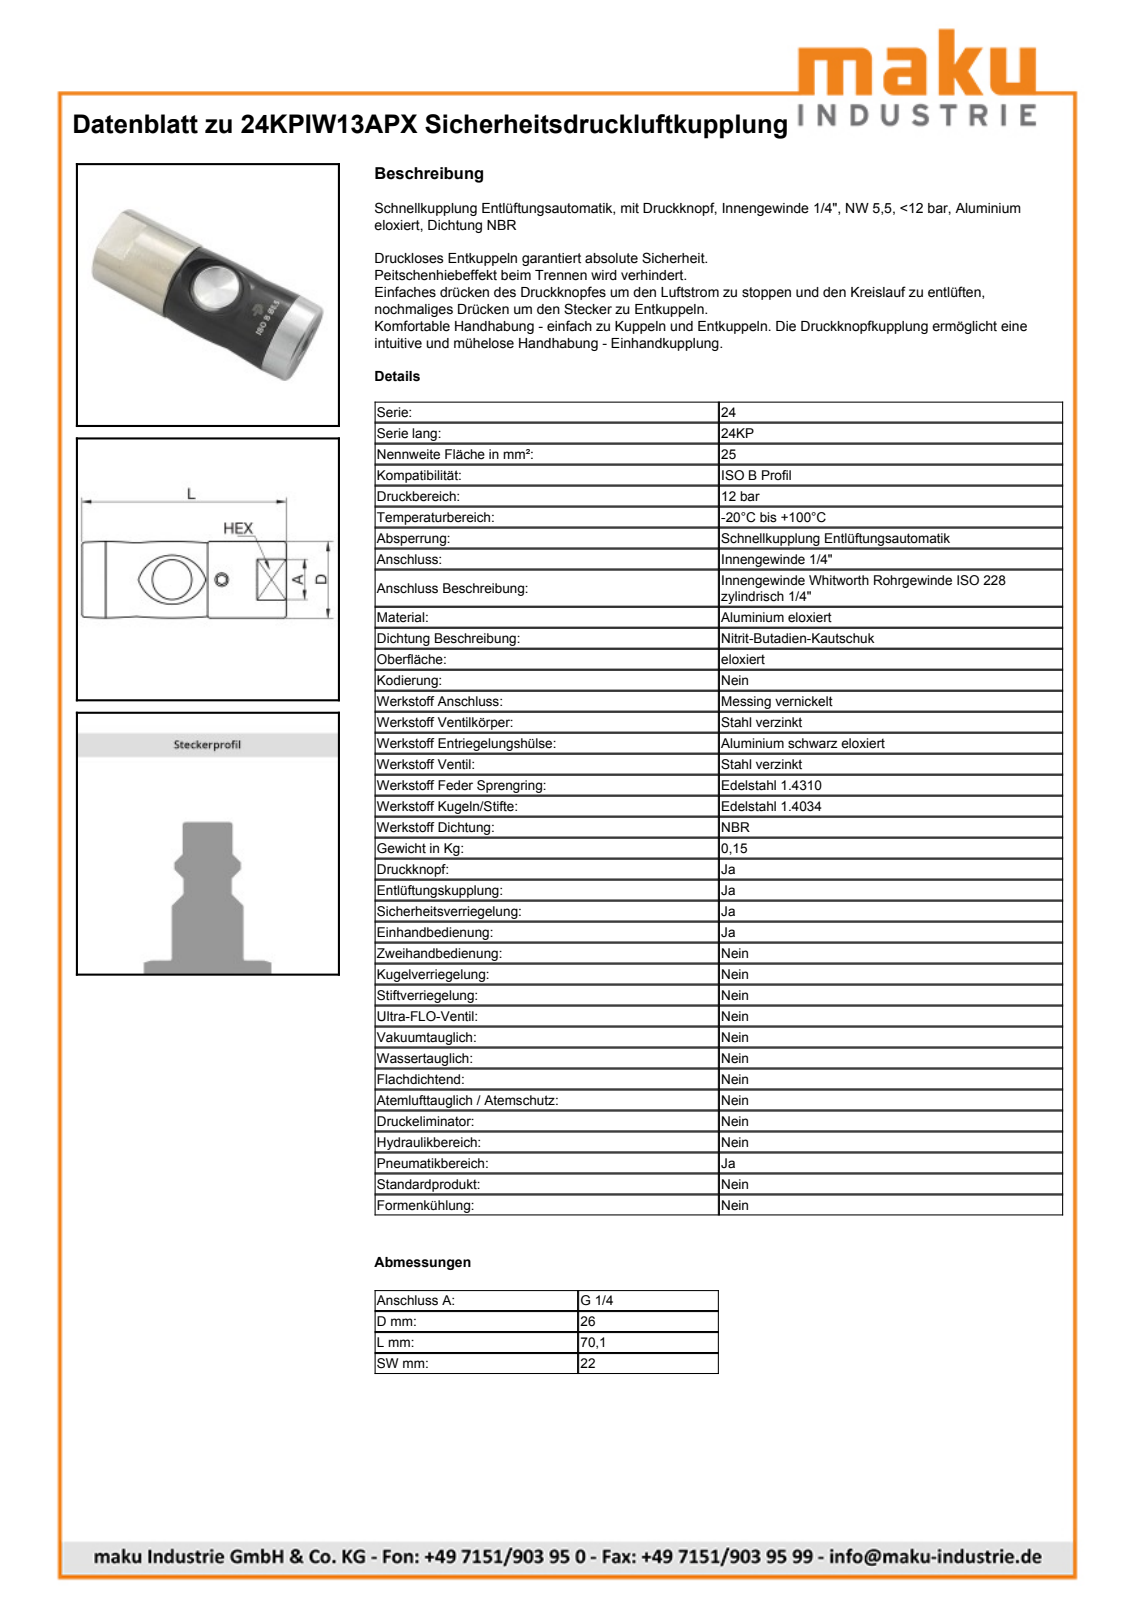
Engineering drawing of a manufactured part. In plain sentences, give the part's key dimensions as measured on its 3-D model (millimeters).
The part is named "24KPIW13APX". Its 3-D file was written by "Autodesk Inventor 2019 (CONFIG_CONTROL_DESIGN)". It is 41 solids with 266 faces: 74 planar, 88 cylindrical and 104 other. Overall it measures 70.1 by 26 by 26 millimeters. Its volume is 39 480 cubic millimeters and its surface area 24 201 square millimeters. Round holes: 2 of diameter 12.4, 1 of diameter 3.5, 1 of diameter 6.5, 1 of diameter 7, 1 of diameter 8.4, 1 of diameter 9.65, 1 of diameter 10.6, 1 of diameter 11.1, 1 of diameter 11.45, 1 of diameter 12.25, 1 of diameter 13.6, 1 of diameter 15. Round bosses or shafts: 1 of diameter 26, 1 of diameter 22, 1 of diameter 21.43, 1 of diameter 18.1, 1 of diameter 16.73, 1 of diameter 16.5, 1 of diameter 15.8, 1 of diameter 12.7. Partial cylindrical surfaces (rounded edges, fillets, slot ends): 2 of radius 6.2, 1 of radius 4.4. The main face-to-face distances are 43.1, 35, 8.1, 27, 62, 70.1, 14.95, 12.05, 49.95, 58.05. The hole center spacings are 0.6, 0.7, 1.3, 17.05.
